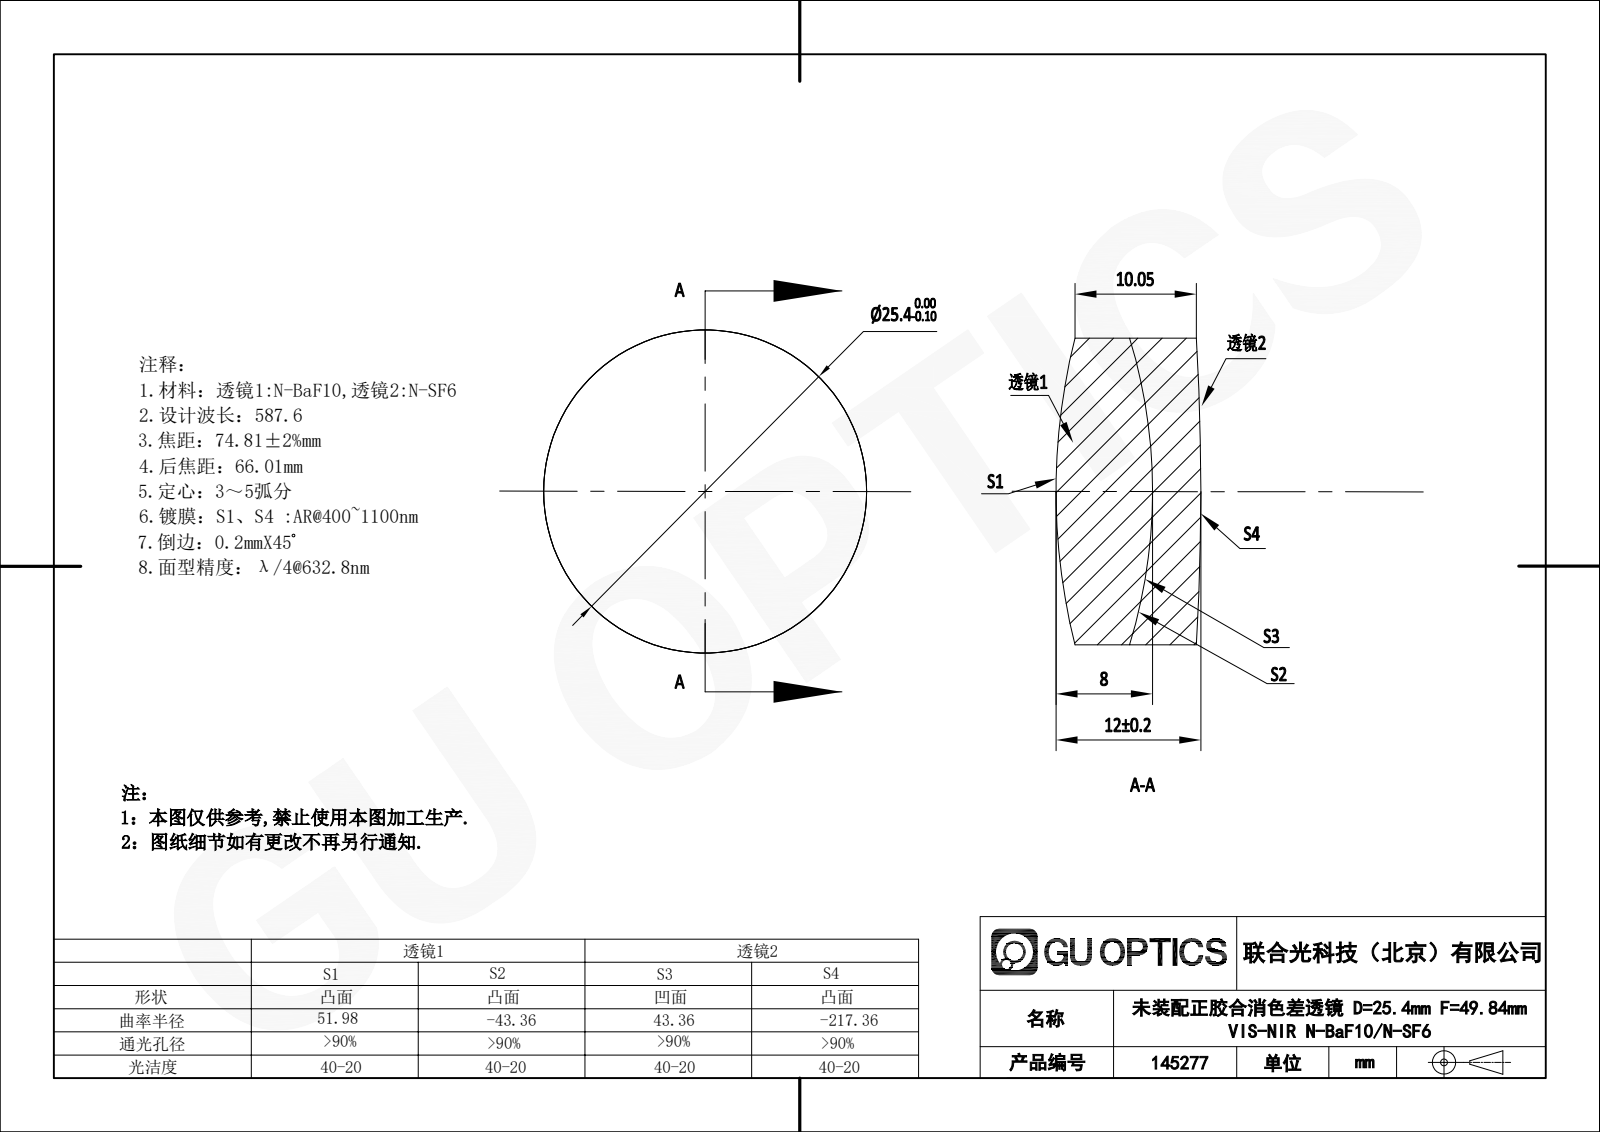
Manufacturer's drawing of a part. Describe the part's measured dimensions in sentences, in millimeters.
The part is named "145277". Its 3-D file was written by "SolidWorks 2020 (CONFIG_CONTROL_DESIGN)". It is 2 solids with 12 faces: 0 planar, 4 cylindrical and 8 other. Overall it measures 25.4 by 25.4 by 12 millimeters. Its volume is 5 589 cubic millimeters and its surface area 2 860 square millimeters. Round bosses or shafts: 1 of diameter 25.4.
